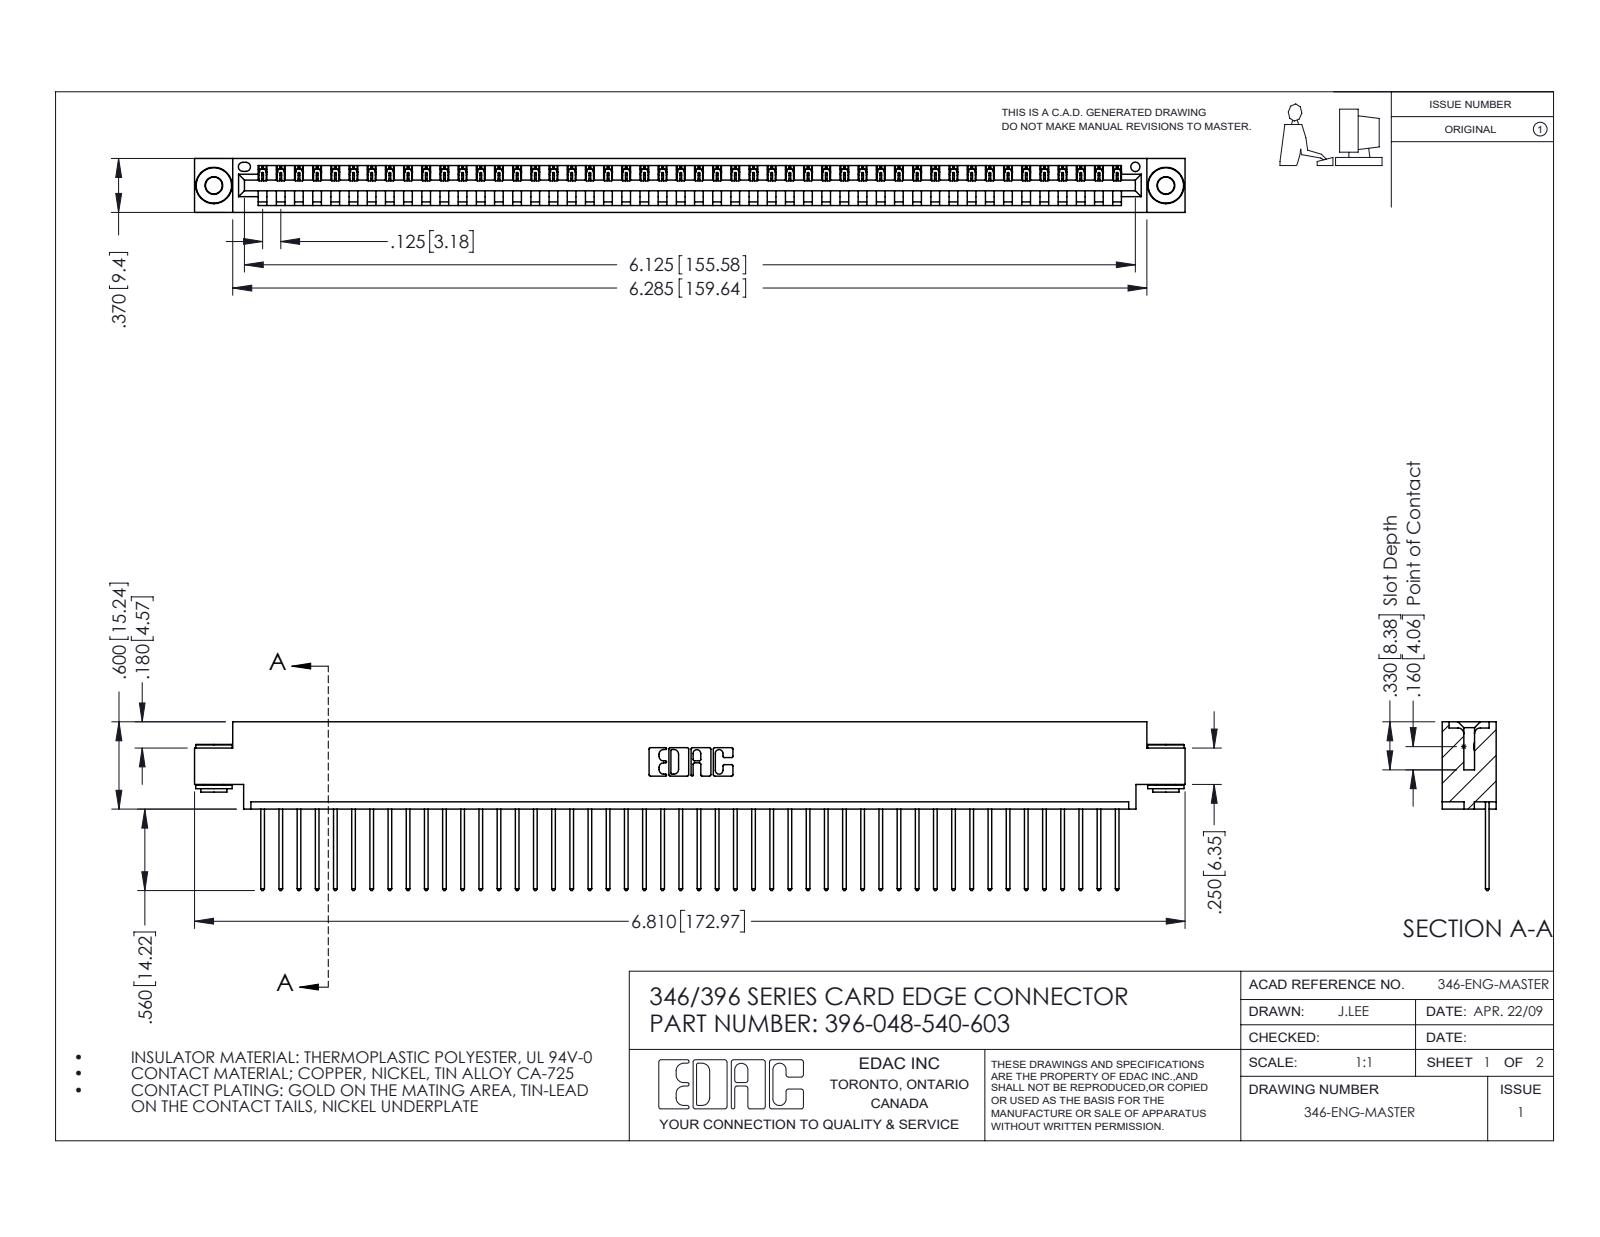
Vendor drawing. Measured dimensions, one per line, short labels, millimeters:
name: 396-048-540-603; 345-292-001_345-293-140; 346 Part_0.170 Offset - 0.156 Dia-TH; 345-250-002_345-250-002-102
written by: SolidWorks 2016 (CONFIG_CONTROL_DESIGN)
unit: mm
bodies: 51 solids, 2948 faces (2010 planar, 930 cylindrical, 8 other)
size: 173 × 29.5 × 9.4
volume: 16 530 mm³; area: 21 570 mm²
holes: 2× ⌀2.9, 2× ⌀4, 1× ⌀1.6
bosses: 2× ⌀6.4, 2× ⌀4.6, 2× ⌀3.5
rounds: 96× R0.2, 96× R0.3, 22× R0.3, 6× R0.2, 6× R0.8, 3× R0.7, 2× R0.8, 2× R1
face distances: 1.2, 8.2, 9.4, 6.4, 0.6, 1.8, 7.6, 3.8, 5.6, 2.5
hole spacings: 6.2, 160.9, 166.2
